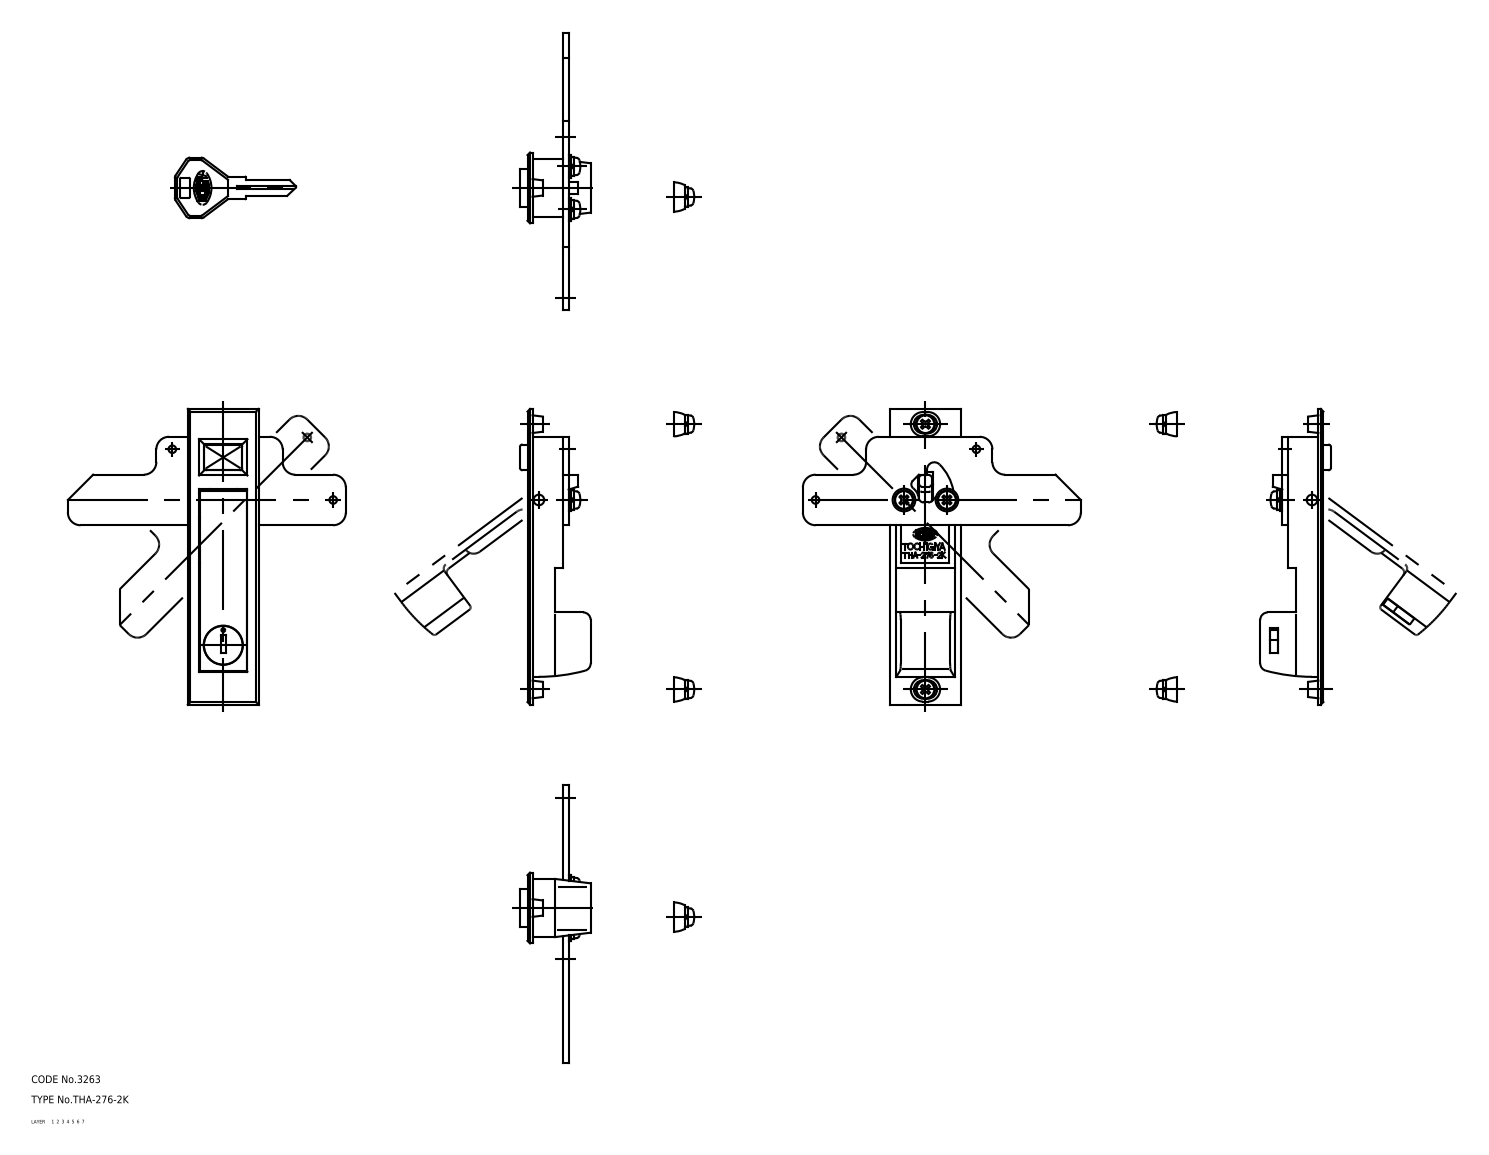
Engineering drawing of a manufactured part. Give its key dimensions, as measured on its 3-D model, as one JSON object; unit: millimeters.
{"part_name": "bracket; screw_B; screw_A; lock (+7 more)", "step_written_by": "CADfix (AUTOMOTIVE_DESIGN)", "units": "millimeters", "bodies": {"solids": 13, "faces": 447, "planar": 0, "cylindrical": 0, "other": 447}, "overall_size": [117, 110, 109.3], "volume_mm3": 37526, "surface_area_mm2": 33469}
